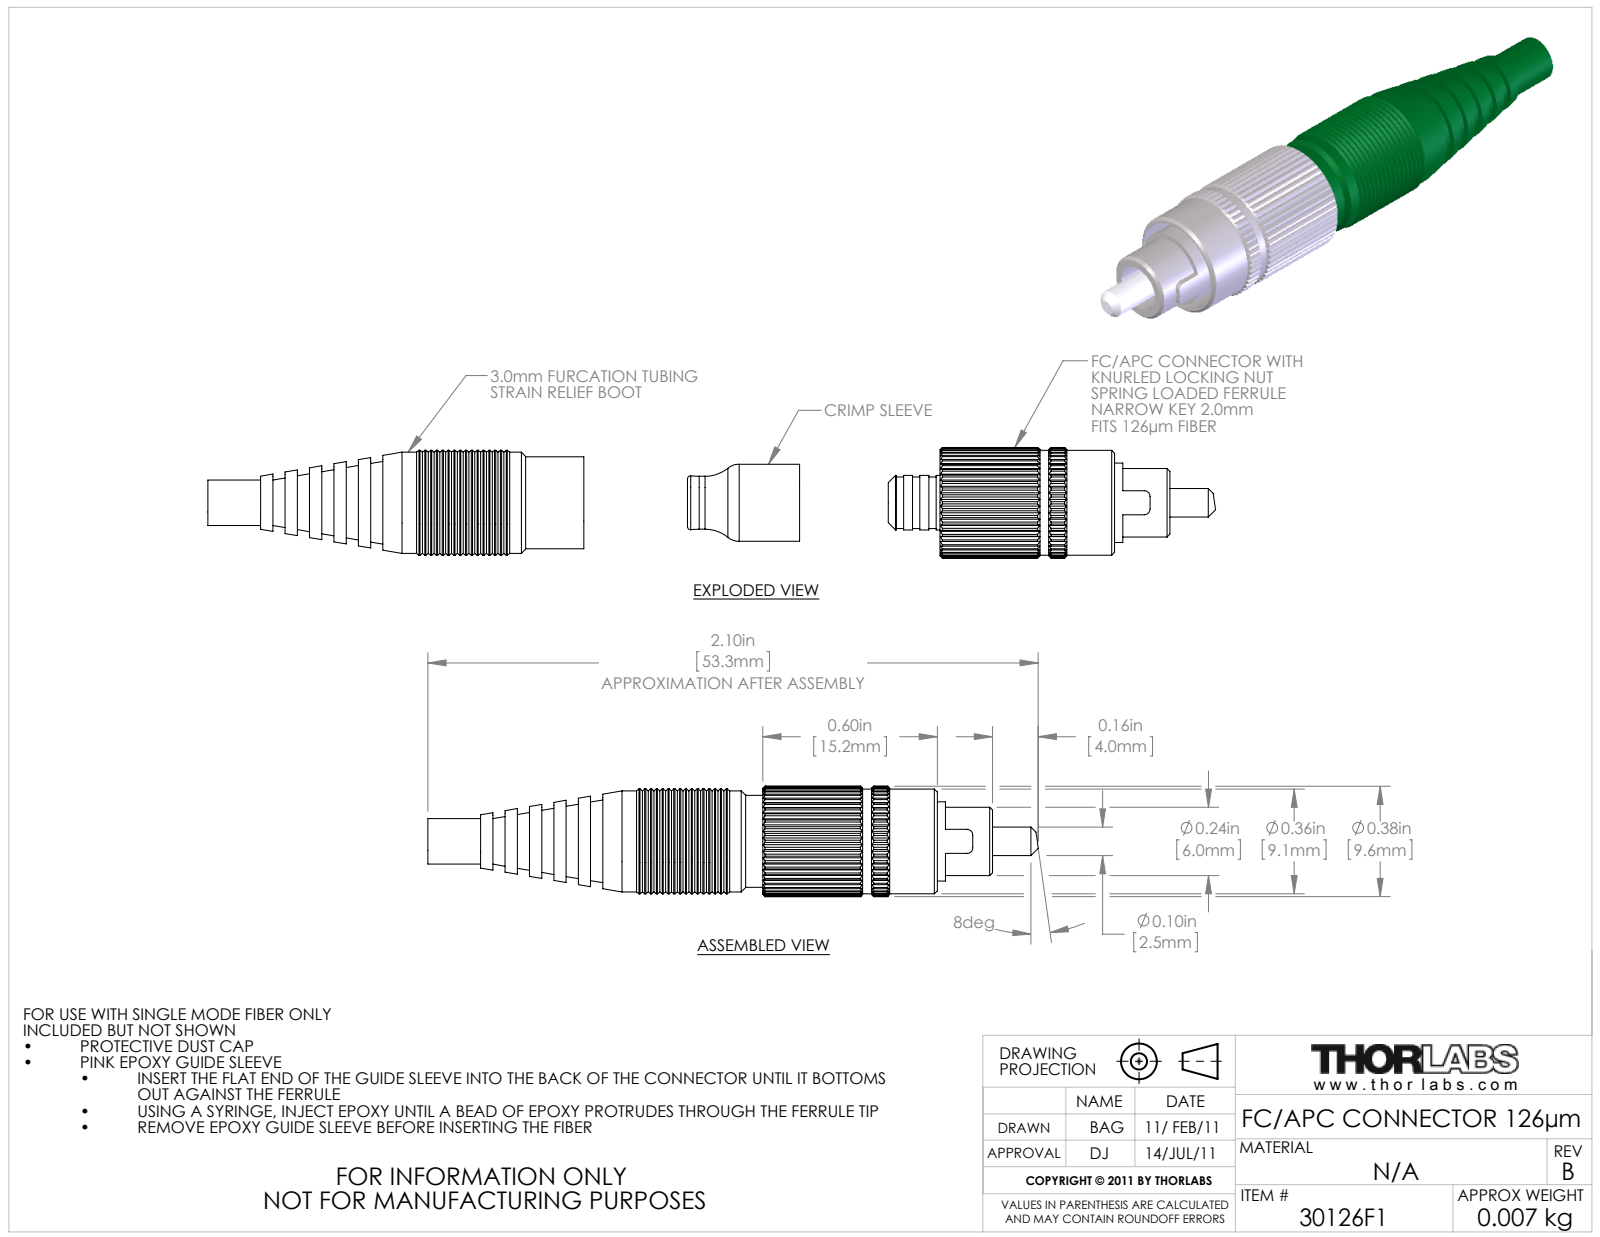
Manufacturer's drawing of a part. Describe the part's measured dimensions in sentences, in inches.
The part is named "2339-E0W". Its 3-D file was written by "SolidWorks 2011 (AUTOMOTIVE_DESIGN)". It is 4 solids with 572 faces: 246 planar, 172 cylindrical and 154 other. Overall it measures 2.098 by 0.38 by 0.38 inches. Its volume is 0.119 cubic inches and its surface area 5.553 square inches. Round holes: 1 of diameter 0.098, 1 of diameter 0.124, 1 of diameter 0.126, 1 of diameter 0.137, 1 of diameter 0.164, 1 of diameter 0.2, 1 of diameter 0.225, 1 of diameter 0.236, 1 of diameter 0.325. Round bosses or shafts: 1 of diameter 0.36, 1 of diameter 0.347, 1 of diameter 0.316, 1 of diameter 0.313, 1 of diameter 0.273, 1 of diameter 0.265, 1 of diameter 0.235, 1 of diameter 0.187. Partial cylindrical surfaces (rounded edges, fillets, slot ends): 2 of radius 0.02, 1 of radius 0.19. The main face-to-face distances are 0.28, 0.042, 0.126, 0.084, 0.168, 0.025, 0.042, 0.084, 0.21, 0.252.
